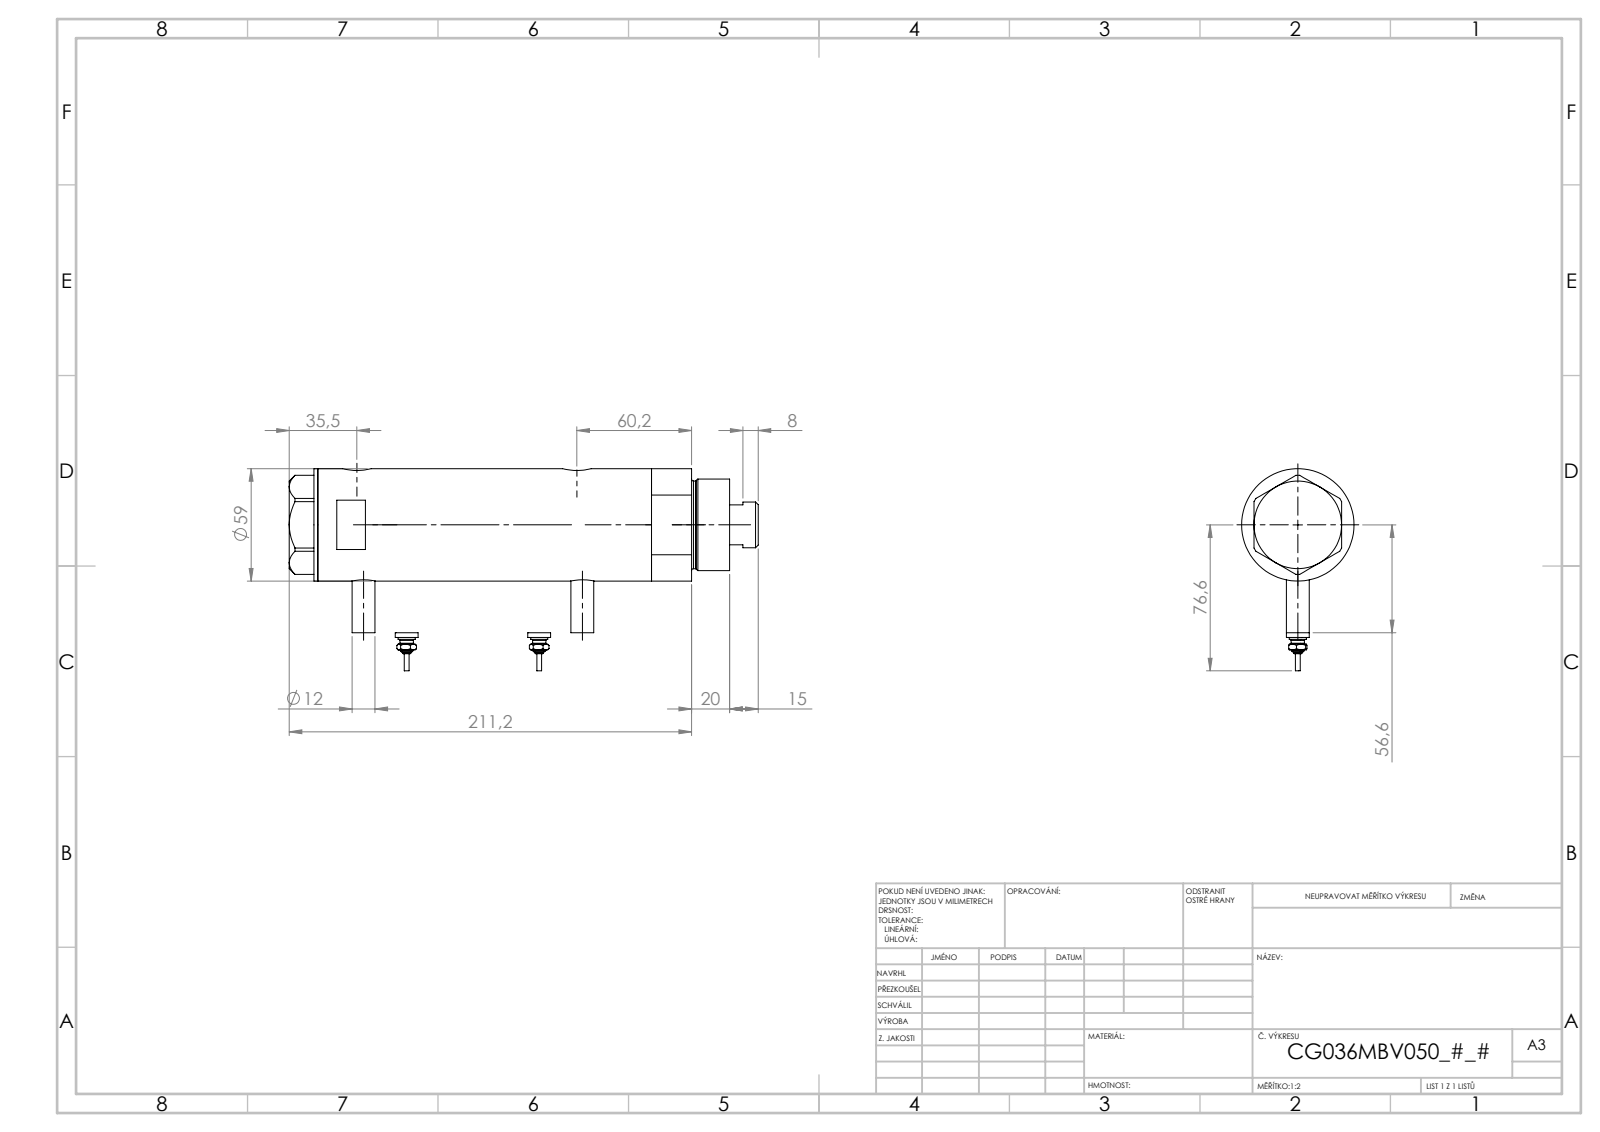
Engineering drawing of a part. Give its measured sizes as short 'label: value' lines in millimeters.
name: V270CG_VC; V270CG_BACK; V270CG_MIDDLE; V270CG_SWITCH (+1 more)
written by: SolidWorks 2019 (CONFIG_CONTROL_DESIGN)
unit: mm
bodies: 6 solids, 232 faces (81 planar, 77 cylindrical, 74 other)
size: 213.42 × 91.3 × 59
volume: 484 346 mm³; area: 102 689 mm²
holes: 2× ⌀5, 2× ⌀9.73, 2× ⌀12.5, 2× ⌀15, 1× ⌀8.5, 1× ⌀25, 1× ⌀26.5, 1× ⌀36, 1× ⌀40, 1× ⌀52
bosses: 3× ⌀12, 2× ⌀9, 2× ⌀7, 2× ⌀4.34, 2× ⌀2.4, 1× ⌀59, 1× ⌀48, 1× ⌀46
face distances: 107.35, 38.5, 122.35, 83.85, 15, 15.01, 23.5, 23.49, 107.34, 183.43
hole spacings: 2.9, 3.5, 82.15, 85.05, 85.65, 88.55, 2.89, 2.91
